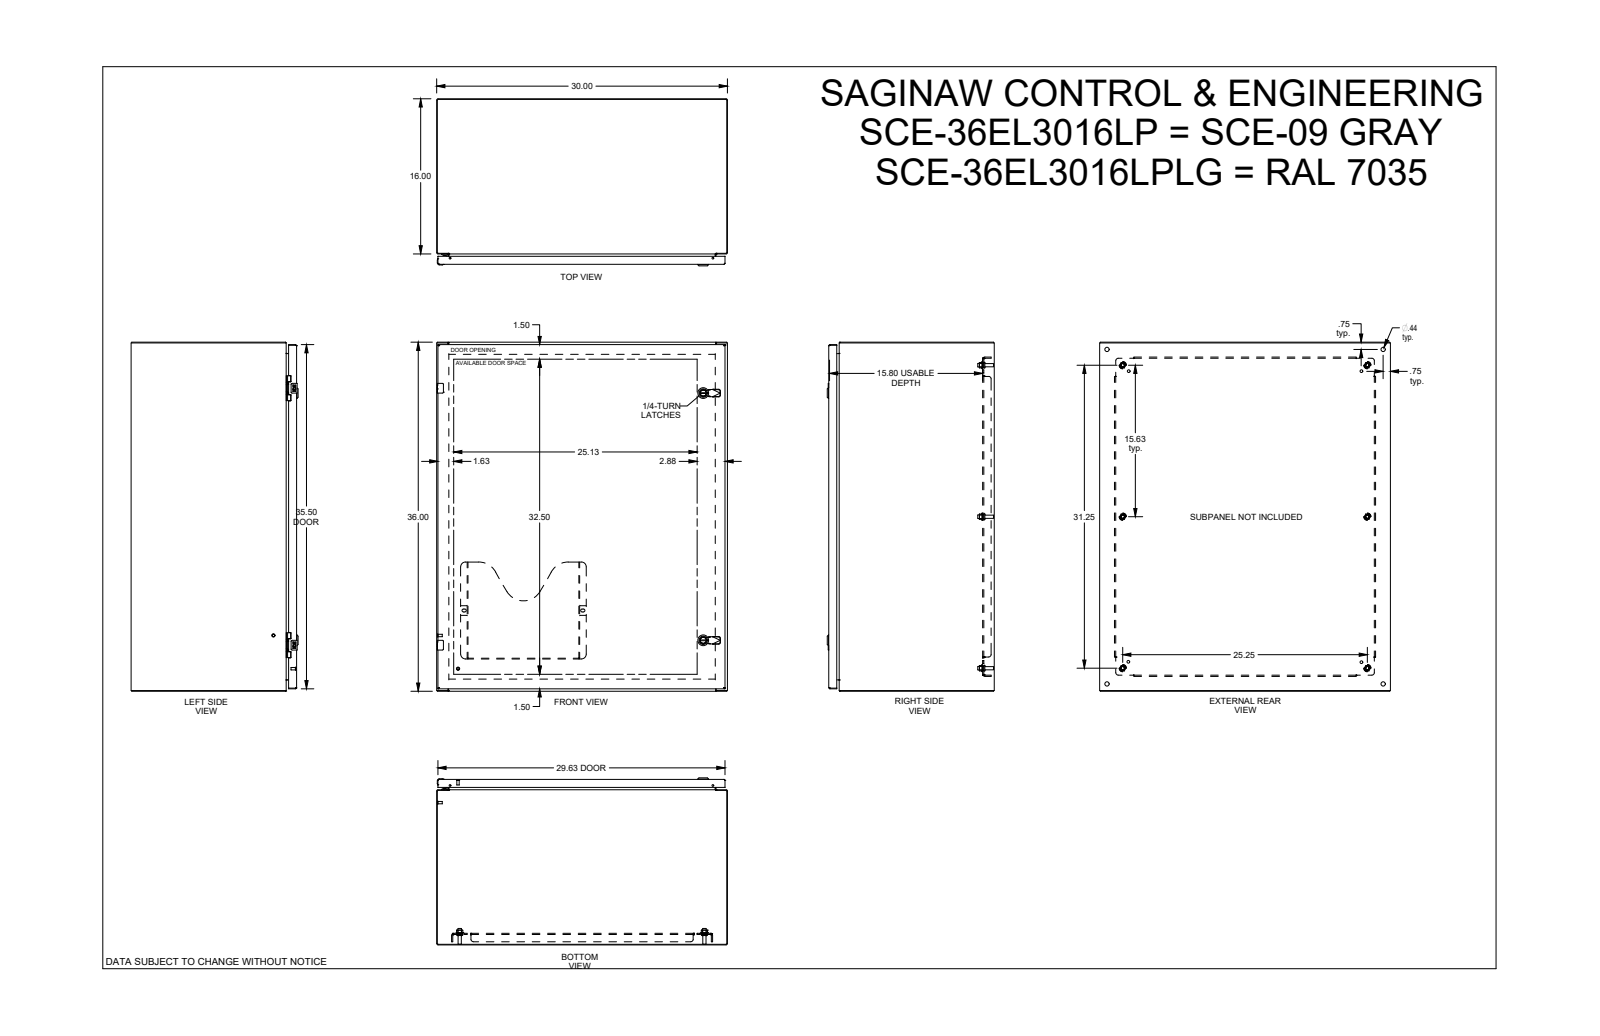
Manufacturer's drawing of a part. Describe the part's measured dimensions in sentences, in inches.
The part is named "SCE-36EL3016LP". Its 3-D file was written by "SolidWorks 2021 (AUTOMOTIVE_DESIGN)". It is 51 solids with 2989 faces: 1139 planar, 888 cylindrical and 962 other. Overall it measures 36 by 30 by 17.23 inches. Its volume is 486.4 cubic inches and its surface area 11 702 square inches. Round holes: 6 of diameter 0.367, 6 of diameter 0.5, 4 of diameter 0.172, 4 of diameter 0.205, 4 of diameter 0.244, 4 of diameter 0.266, 4 of diameter 0.281, 4 of diameter 0.375, 4 of diameter 0.437, 2 of diameter 0.04, 2 of diameter 0.188, 2 of diameter 0.197. Round bosses or shafts: 6 of diameter 0.366, 6 of diameter 0.332, 6 of diameter 0.17, 4 of diameter 0.25, 4 of diameter 0.248, 4 of diameter 0.24, 3 of diameter 0.196, 2 of diameter 1.102. Partial cylindrical surfaces (rounded edges, fillets, slot ends): 56 of radius 0.012, 40 of radius 0.01, 20 of radius 0.015, 20 of radius 0.02, 17 of radius 0.04, 13 of radius 0.06, 12 of radius 0.029, 12 of radius 0.1. The main face-to-face distances are 0.075, 0.06, 29.925, 0.075, 17.073, 16.998, 17.013, 16.938, 1.2, 15.873. The hole center spacings are 0.985, 26.5, 15.625, 32.915, 42.462, 0.02, 0.493, 0.494.
